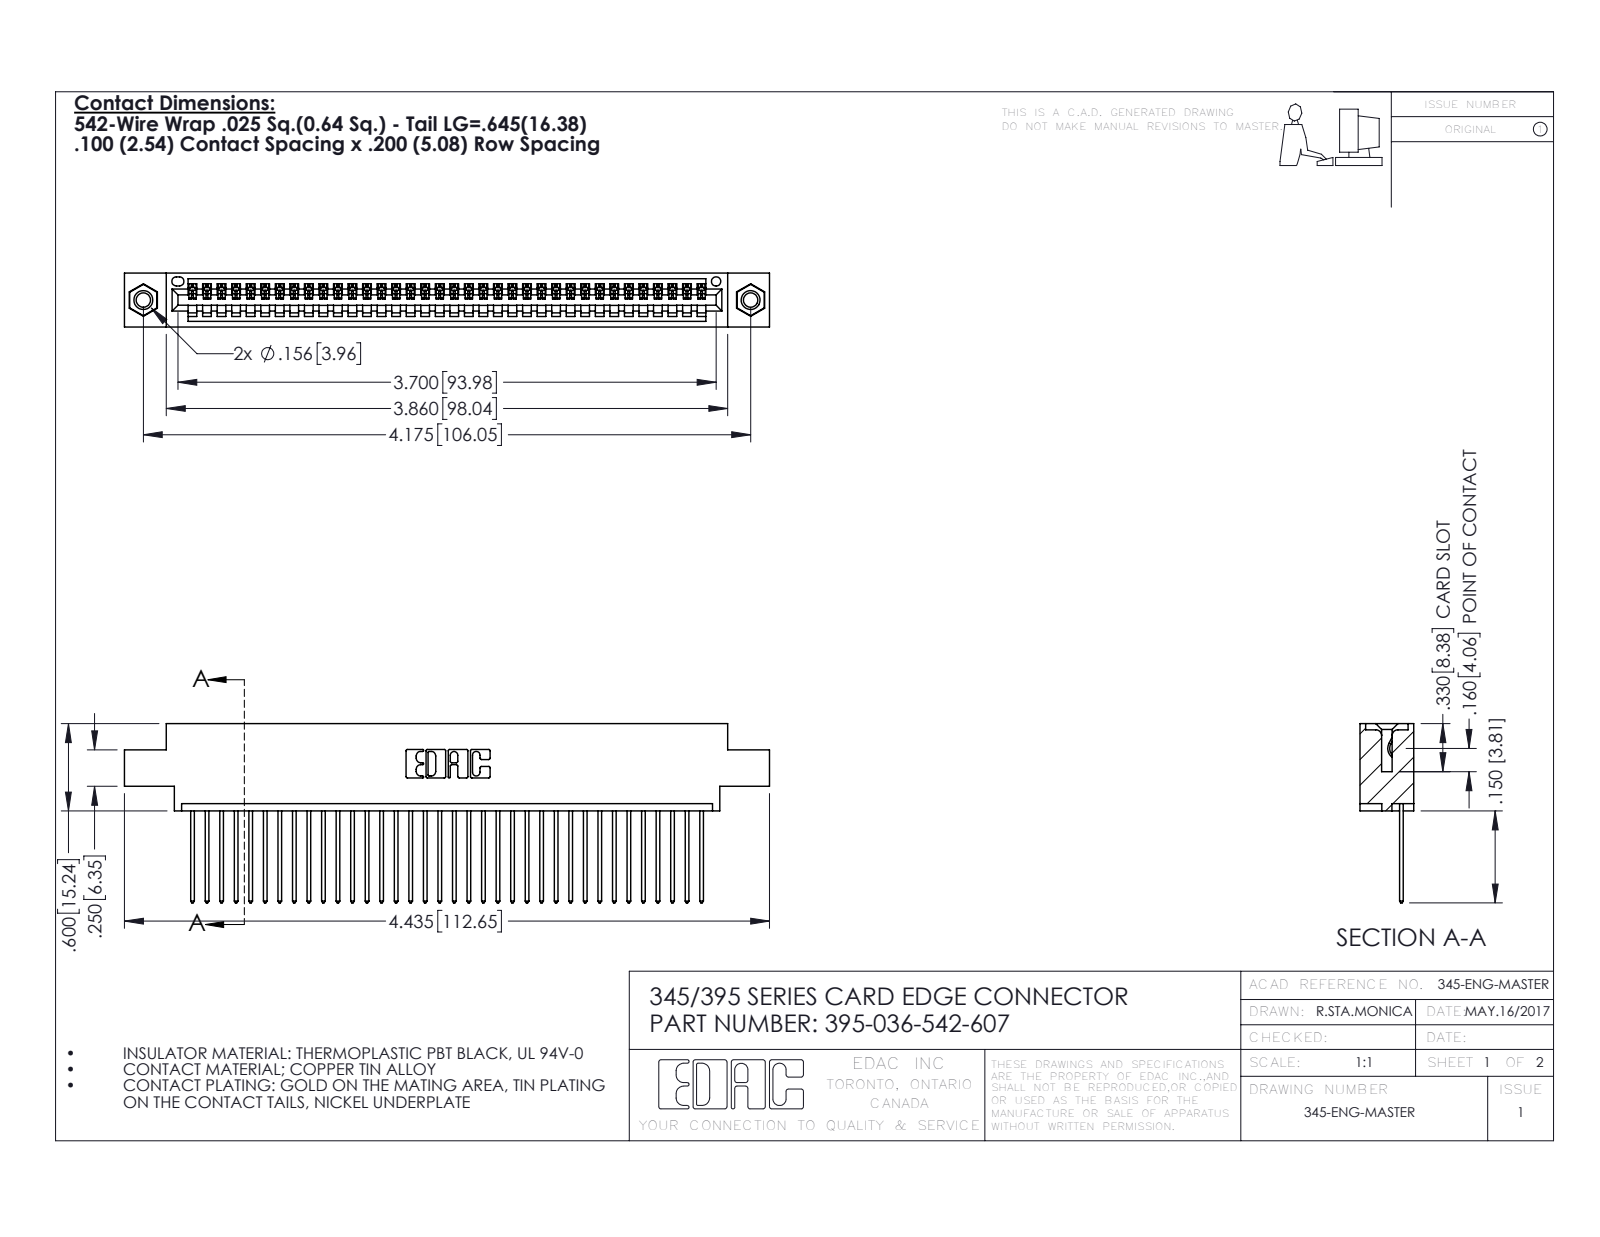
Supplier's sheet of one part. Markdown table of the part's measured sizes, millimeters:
| quantity | value |
| --- | --- |
| part name | 345-250-001_345-250-005-103; 395-036-542-607; 345-292-001_345-293-142; 345 Part_0.170 Offset - 0.156 Dia-TI |
| STEP written by | SolidWorks 2016 (CONFIG_CONTROL_DESIGN) |
| units | millimeters |
| bodies | 39 solids, 2278 faces (1556 planar, 706 cylindrical, 16 other) |
| overall size | 112.6 × 31.3 × 9.4 |
| volume | 10 600 mm³ |
| surface area | 14 680 mm² |
| round holes (diameter × count) | 2.5 × 2, 3.2 × 2, 4 × 2, 1.6 × 1 |
| round bosses / shafts (diameter × count) | 3.9 × 2 |
| partial cylindrical surfaces (radius × count) | 0.2 × 72, 0.3 × 72, 0.3 × 22, 0.2 × 6, 0.8 × 6, 0.7 × 3, 0.8 × 2, 1 × 2 |
| main face-to-face distances | 1.8, 7.6, 9.4, 2.5, 6.9, 0.6, 5.1, 5.7, 4.4, 3.8 |
| hole center spacings | 6.9, 100.1, 106 |
